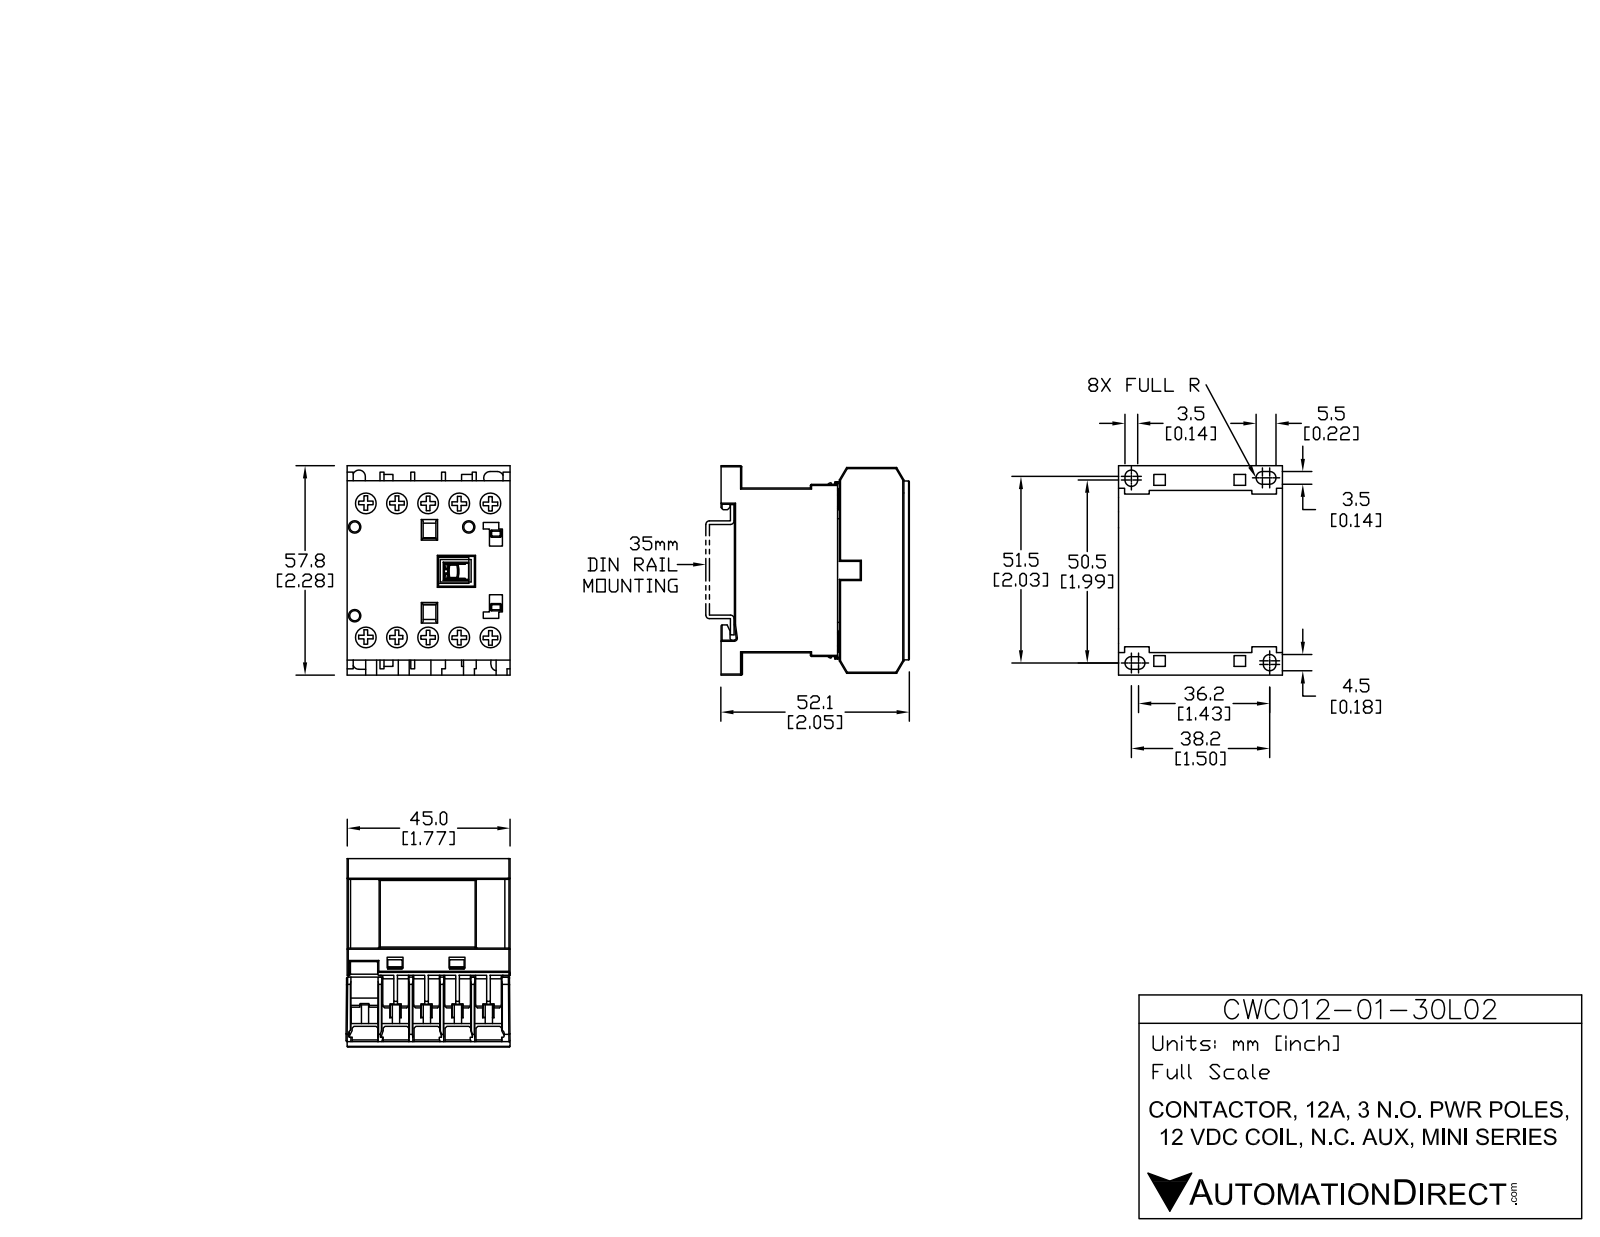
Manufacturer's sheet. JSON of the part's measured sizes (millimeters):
{"part_name": "CWC12-01-30L02", "step_written_by": "SolidWorks 2013 (AUTOMOTIVE_DESIGN)", "units": "millimeters", "bodies": {"solids": 15, "faces": 535, "planar": 445, "cylindrical": 90, "other": 0}, "overall_size": [58.04, 52.12, 45.75], "volume_mm3": 97133, "surface_area_mm2": 30437, "round_holes": [[6.2, 10], [2.8, 3]], "round_bosses_or_shafts": [[5.9, 10]], "partial_cylinders_radius": [[0.3, 20], [1.72, 6], [1.73, 2], [0.32, 1], [0.42, 1], [0.55, 1]], "face_to_face_distances": [8.25, 45.5, 1.25, 16.5, 9.5, 5.5, 17.75, 5.13, 10.63, 7], "hole_center_spacings": [8.55, 37.94, 17.1, 40.72, 36.96, 25.65, 44.99, 6.91]}
